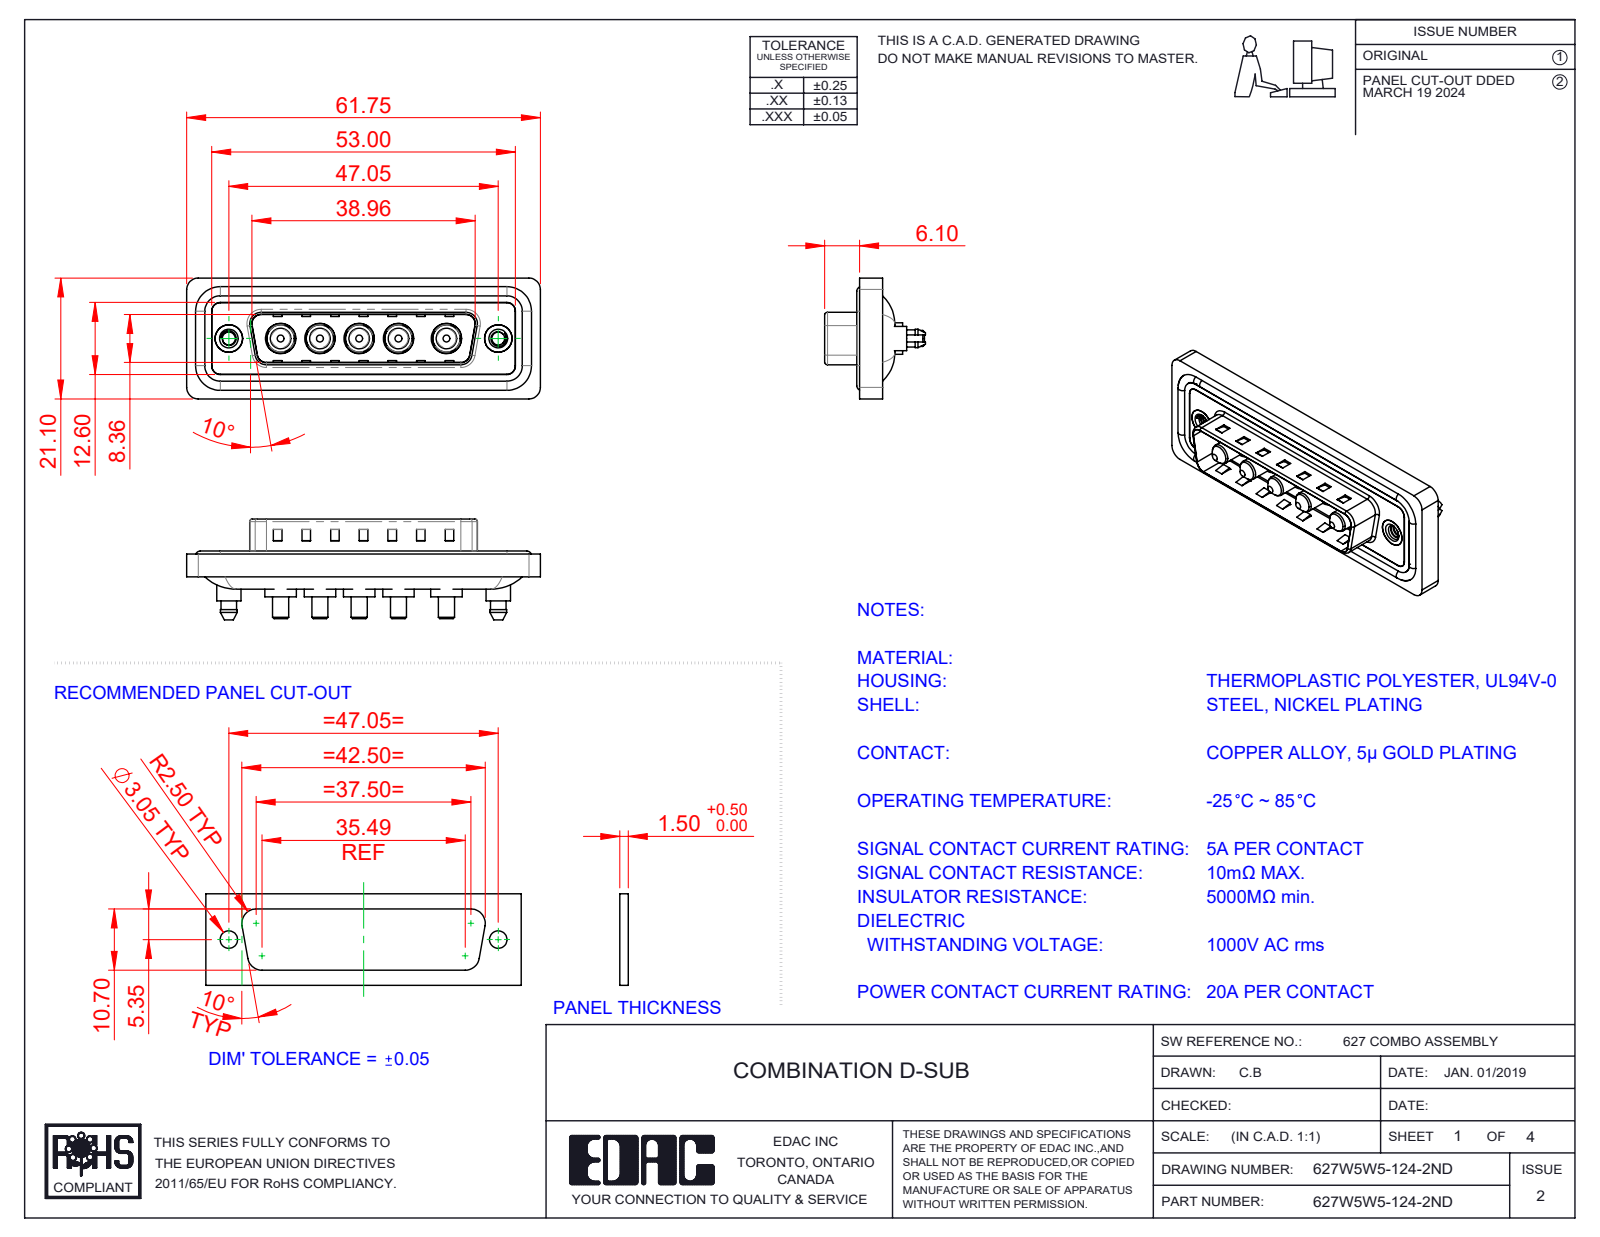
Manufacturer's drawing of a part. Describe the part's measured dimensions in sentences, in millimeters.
The part is named "Power Pin_20A S; 627Combo Threaded Boardlock_5; 627Combo Shell Front_25 Contacts; 627Combo Shell Rear_25 Contacts (+4 more)". Its 3-D file was written by "SolidWorks 2023 (CONFIG_CONTROL_DESIGN)". It is 17 solids with 736 faces: 275 planar, 323 cylindrical and 138 other. Overall it measures 61.75 by 21.1 by 17.6 millimeters. Its volume is 7 607 cubic millimeters and its surface area 12 132 square millimeters. Round holes: 5 of diameter 4.85, 5 of diameter 5.3, 2 of diameter 2.26, 2 of diameter 4, 2 of diameter 4.8, 2 of diameter 5. Round bosses or shafts: 5 of diameter 5.5, 5 of diameter 5.2, 5 of diameter 4.75, 5 of diameter 3.75, 5 of diameter 3.6, 5 of diameter 2.8, 4 of diameter 1.6, 2 of diameter 5.4. Partial cylindrical surfaces (rounded edges, fillets, slot ends): 24 of radius 1.5, 18 of radius 2, 10 of radius 1.6, 8 of radius 0.5, 5 of radius 2.1, 4 of radius 0.25, 4 of radius 0.6, 4 of radius 0.65. The main face-to-face distances are 0.4, 1.5, 3.1, 1.1, 0.5, 1.6, 2.9, 0.82, 9.58, 5.65. The hole center spacings are 6.86, 9.04, 13.73, 38.01, 6.87, 8.37, 8.38, 9.05.
